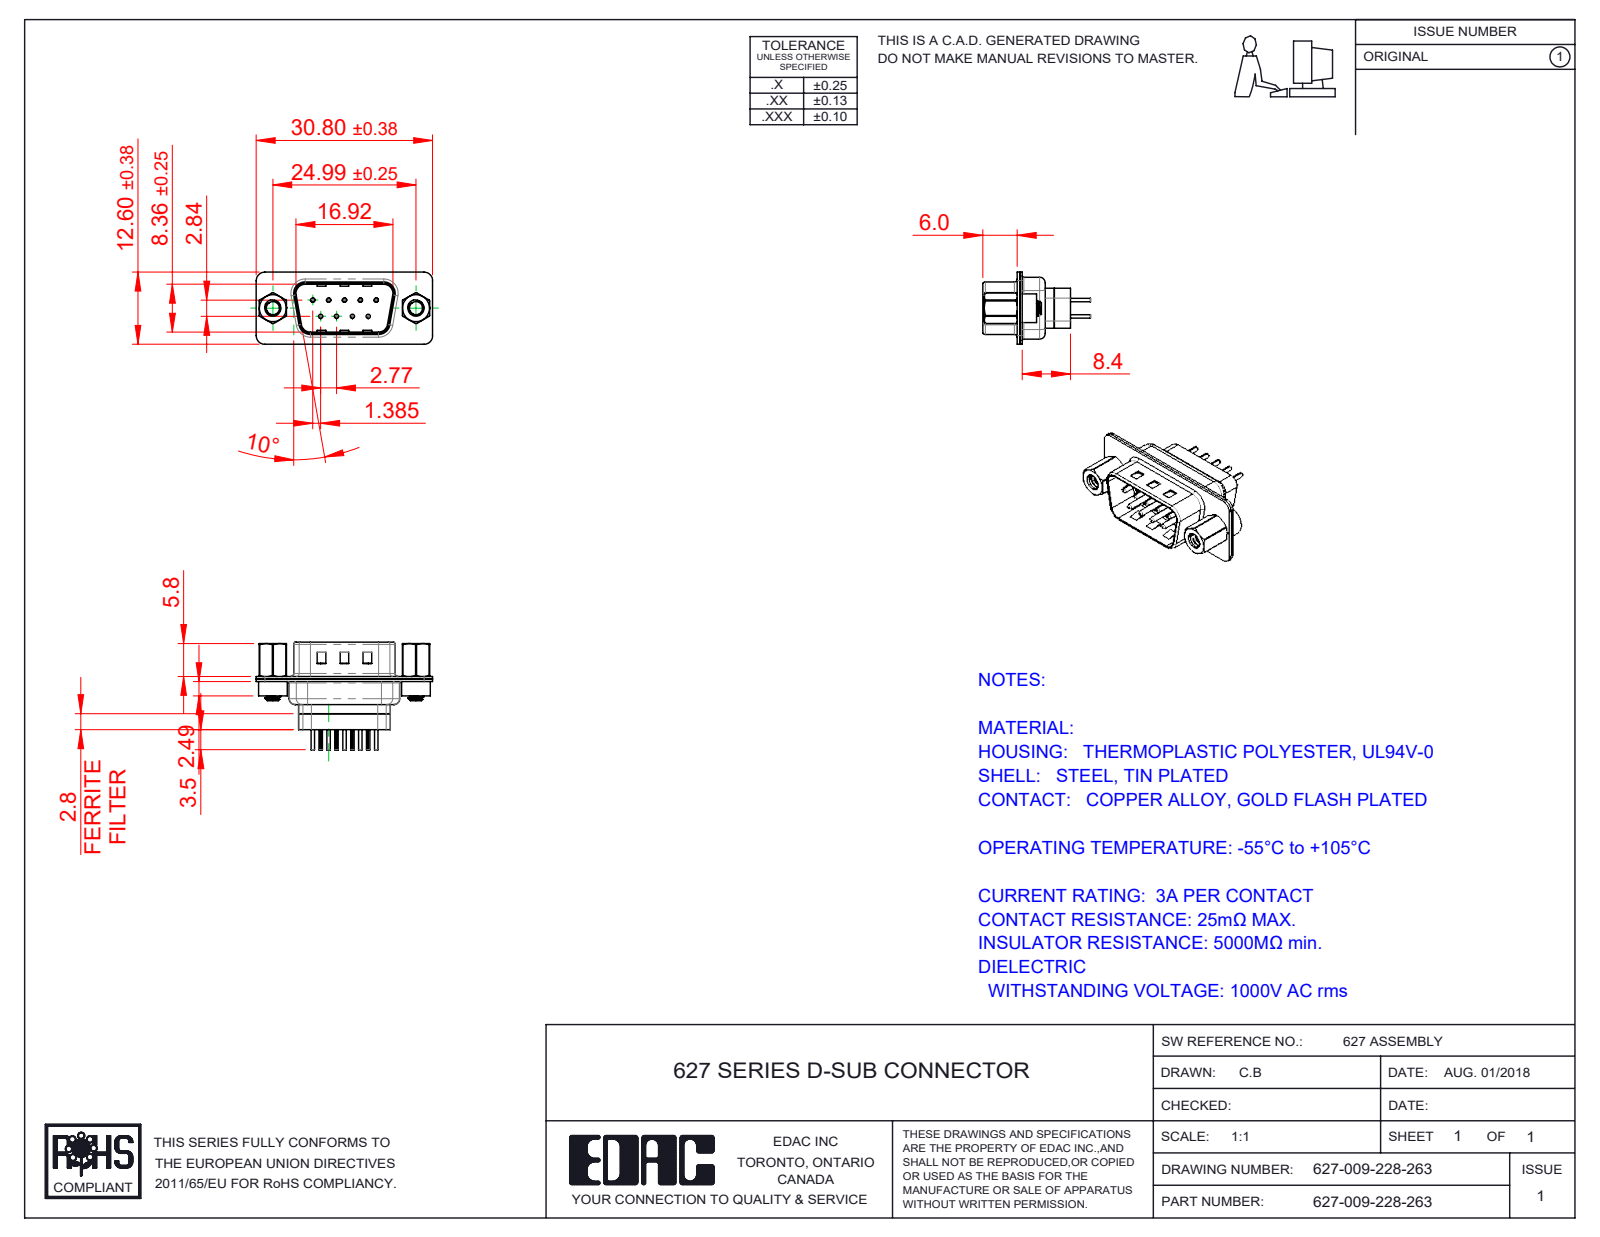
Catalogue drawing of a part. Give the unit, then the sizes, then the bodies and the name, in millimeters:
Units: millimetres
Overall size (bounding box): 30.8 × 18.8 × 12.6
Round holes (diameter × count): ⌀0.2 ×9, ⌀0.35 ×9, ⌀1.1 ×9, ⌀1.6 ×9, ⌀2.26 ×2, ⌀2.29 ×2, ⌀4 ×2, ⌀4.8 ×2
Round bosses / shafts (diameter × count): ⌀2 ×9, ⌀1.5 ×9, ⌀0.75 ×9, ⌀0.6 ×9, ⌀5 ×2, ⌀4.9 ×2, ⌀2.79 ×2
Partial cylindrical surfaces — rounded edges, fillets, slot ends (radius × count): R0.1 ×18, R1.5 ×18, R2 ×12, R0.5 ×8, R1.6 ×8, R0.25 ×4, R0.6 ×4, R0.65 ×4
Main face-to-face distances: 0.4, 0.45, 0.9, 6.5, 6.05, 5.6, 0.82, 9.58, 8.4, 1.4
Hole centre spacings: 3.16, 2.77, 5.54, 5.03, 5.04, 8.31, 7.48, 7.49
Volume: 1 767 mm³ · Surface area: 4 864 mm²
Bodies: 17 solids, 1337 faces (351 planar, 555 cylindrical, 431 other)
Part name (STEP PRODUCT): 627 Contact Row 2_28L; 627 4-40 Hex Standoff; 627 Housing_09 FF; 627 Shell Rear_09 Contacts (+4 more)
STEP written by: SolidWorks 2020 (CONFIG_CONTROL_DESIGN)
